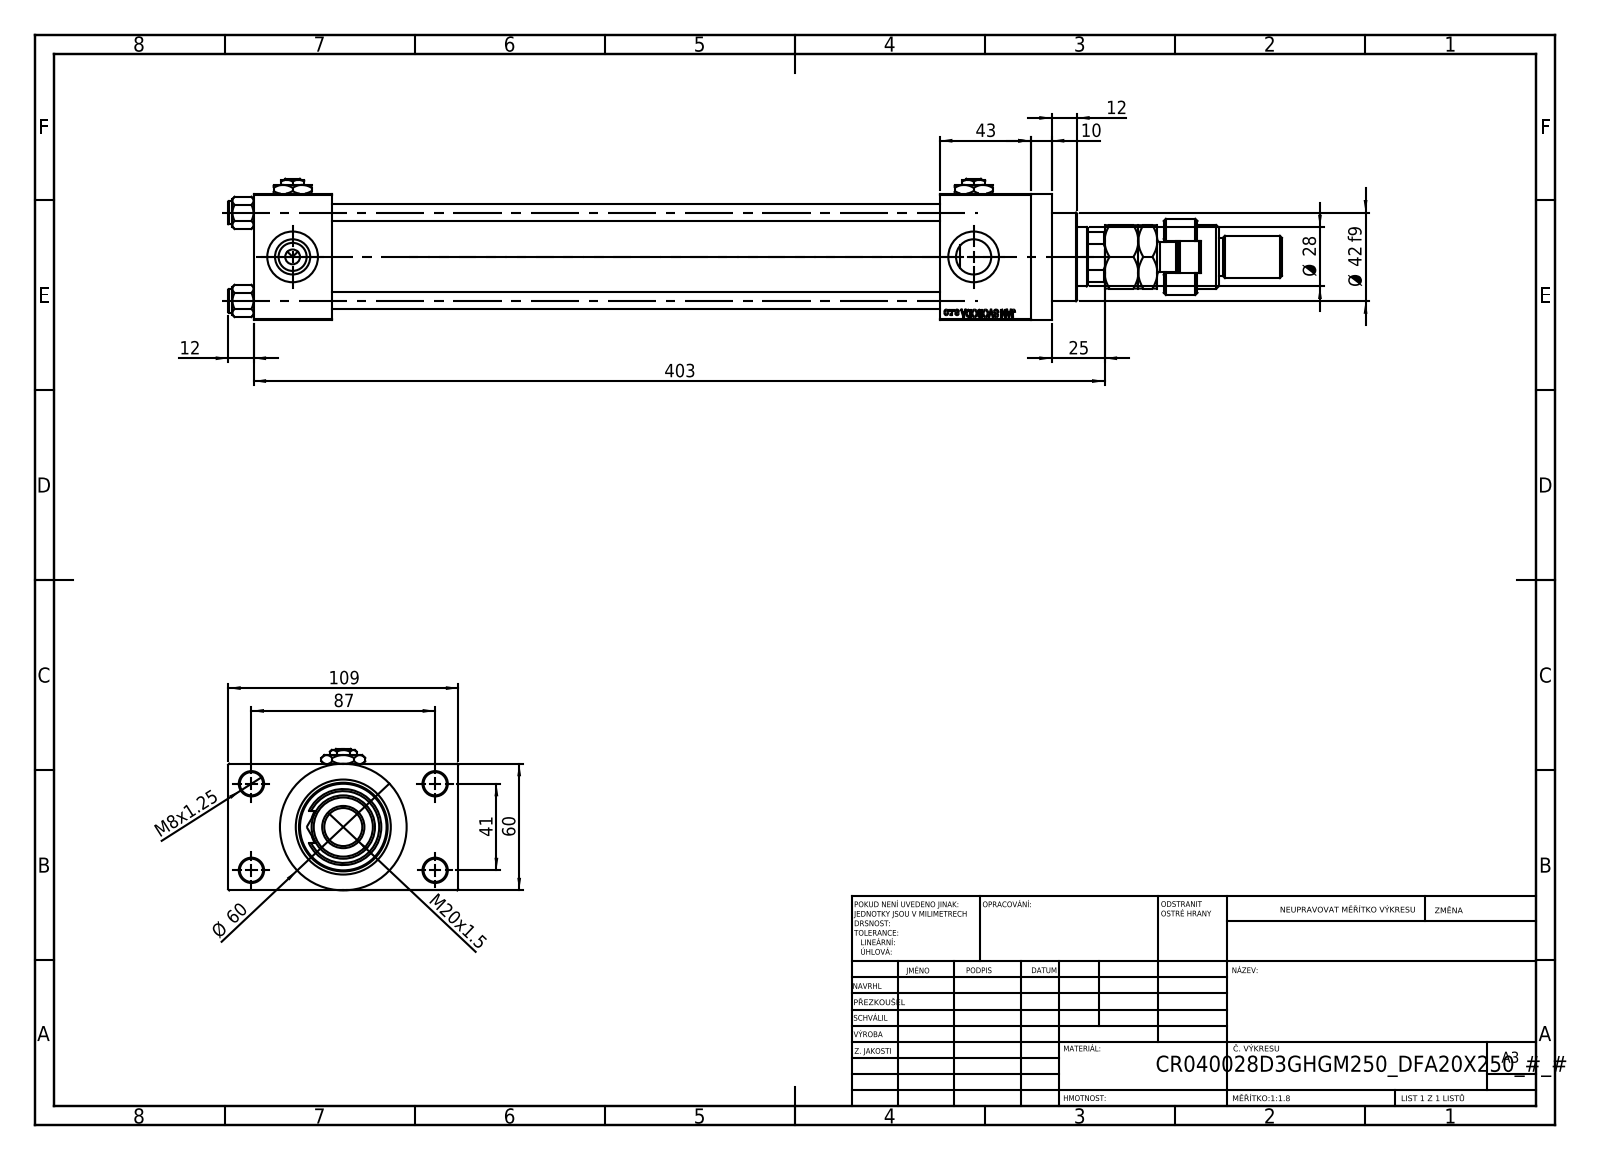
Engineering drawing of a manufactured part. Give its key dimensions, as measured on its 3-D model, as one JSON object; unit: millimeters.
{"part_name": "MFA; V215CR_D_Body; FEMALE_PART_FOR_DFA; V215CR_VCP_D (+4 more)", "step_written_by": "SolidWorks 2019 (CONFIG_CONTROL_DESIGN)", "units": "millimeters", "bodies": {"solids": 15, "faces": 1290, "planar": 574, "cylindrical": 112, "other": 604}, "overall_size": [499, 109, 67], "volume_mm3": 856688, "surface_area_mm2": 250489, "round_holes": [[8, 4], [11, 4], [16.66, 4], [24, 4], [7, 3], [18.5, 1], [28, 1], [31, 1], [40, 1], [45, 1]], "round_bosses_or_shafts": [[11, 4], [60, 1], [46, 1], [42, 1], [36, 1], [30, 1], [22, 1], [20, 1]], "partial_cylinders_radius": [[7.5, 1], [12, 1], [13.5, 1]], "face_to_face_distances": [60, 24.5, 288, 84.5, 37, 325, 43, 368, 331, 10], "hole_center_spacings": [22.65, 29.49, 41.7, 47.15, 48.09, 64.35, 76.49, 41]}
